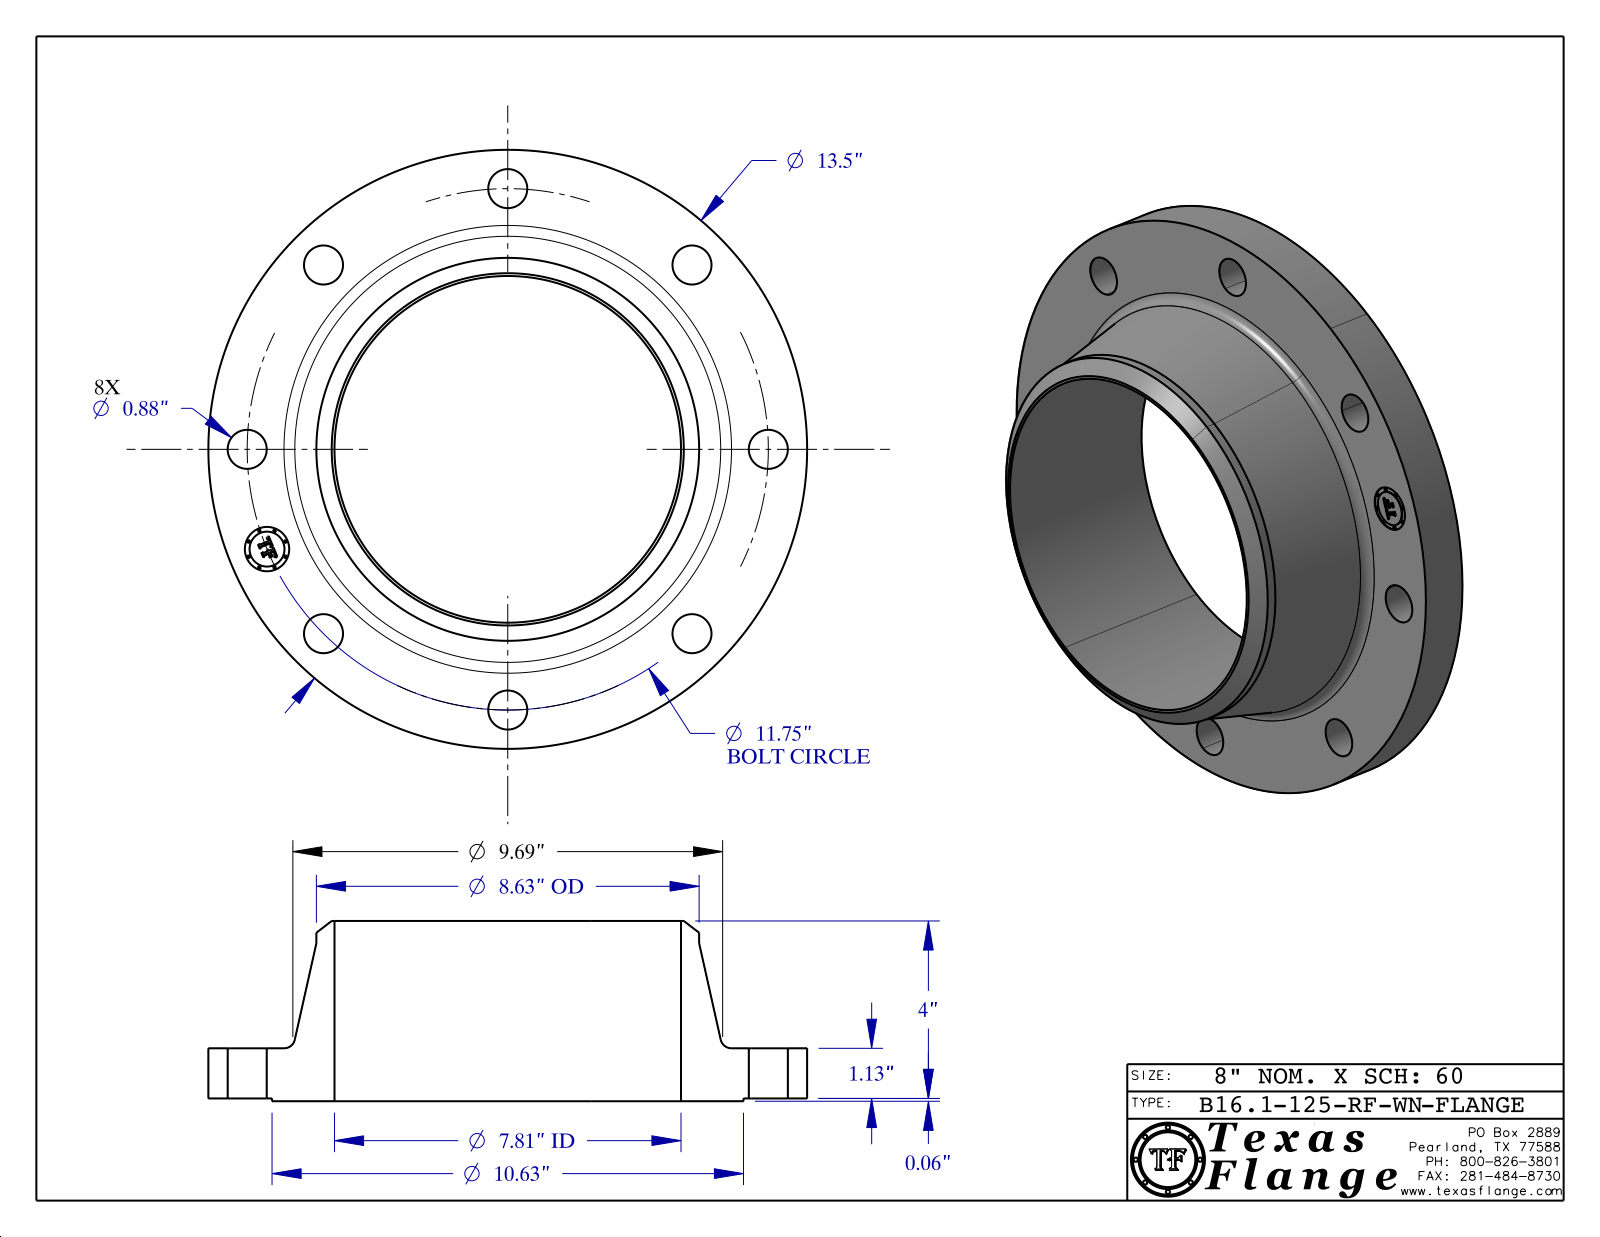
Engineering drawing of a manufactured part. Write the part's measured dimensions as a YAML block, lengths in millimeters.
part_name: "B16.1, Class 125-RF-WN"
step_written_by: "CATIA V5 STEP AP214 (AUTOMOTIVE_DESIGN)"
units: millimeters
bodies: {solids: 1, faces: 419, planar: 369, cylindrical: 44, other: 6}
overall_size: [342.9, 342.9, 103.2]
volume: 2486000
surface_area: 269000
round_holes:
  - {diameter: 22.4, count: 8}
  - {diameter: 25.4, count: 1}
  - {diameter: 198.5, count: 1}
round_bosses_or_shafts:
  - {diameter: 1.5, count: 8}
  - {diameter: 342.9, count: 1}
  - {diameter: 270, count: 1}
  - {diameter: 219.2, count: 1}
  - {diameter: 20, count: 1}
face_to_face_distances: [28.7, 1.6, 30.3, 103.2, 101.6, 72.9, 29.9, 28.3, 0.4, 73.3]
hole_center_spacings: [149.2, 114.2, 211, 275.7, 298.5, 248.2, 58.2, 58.2]
